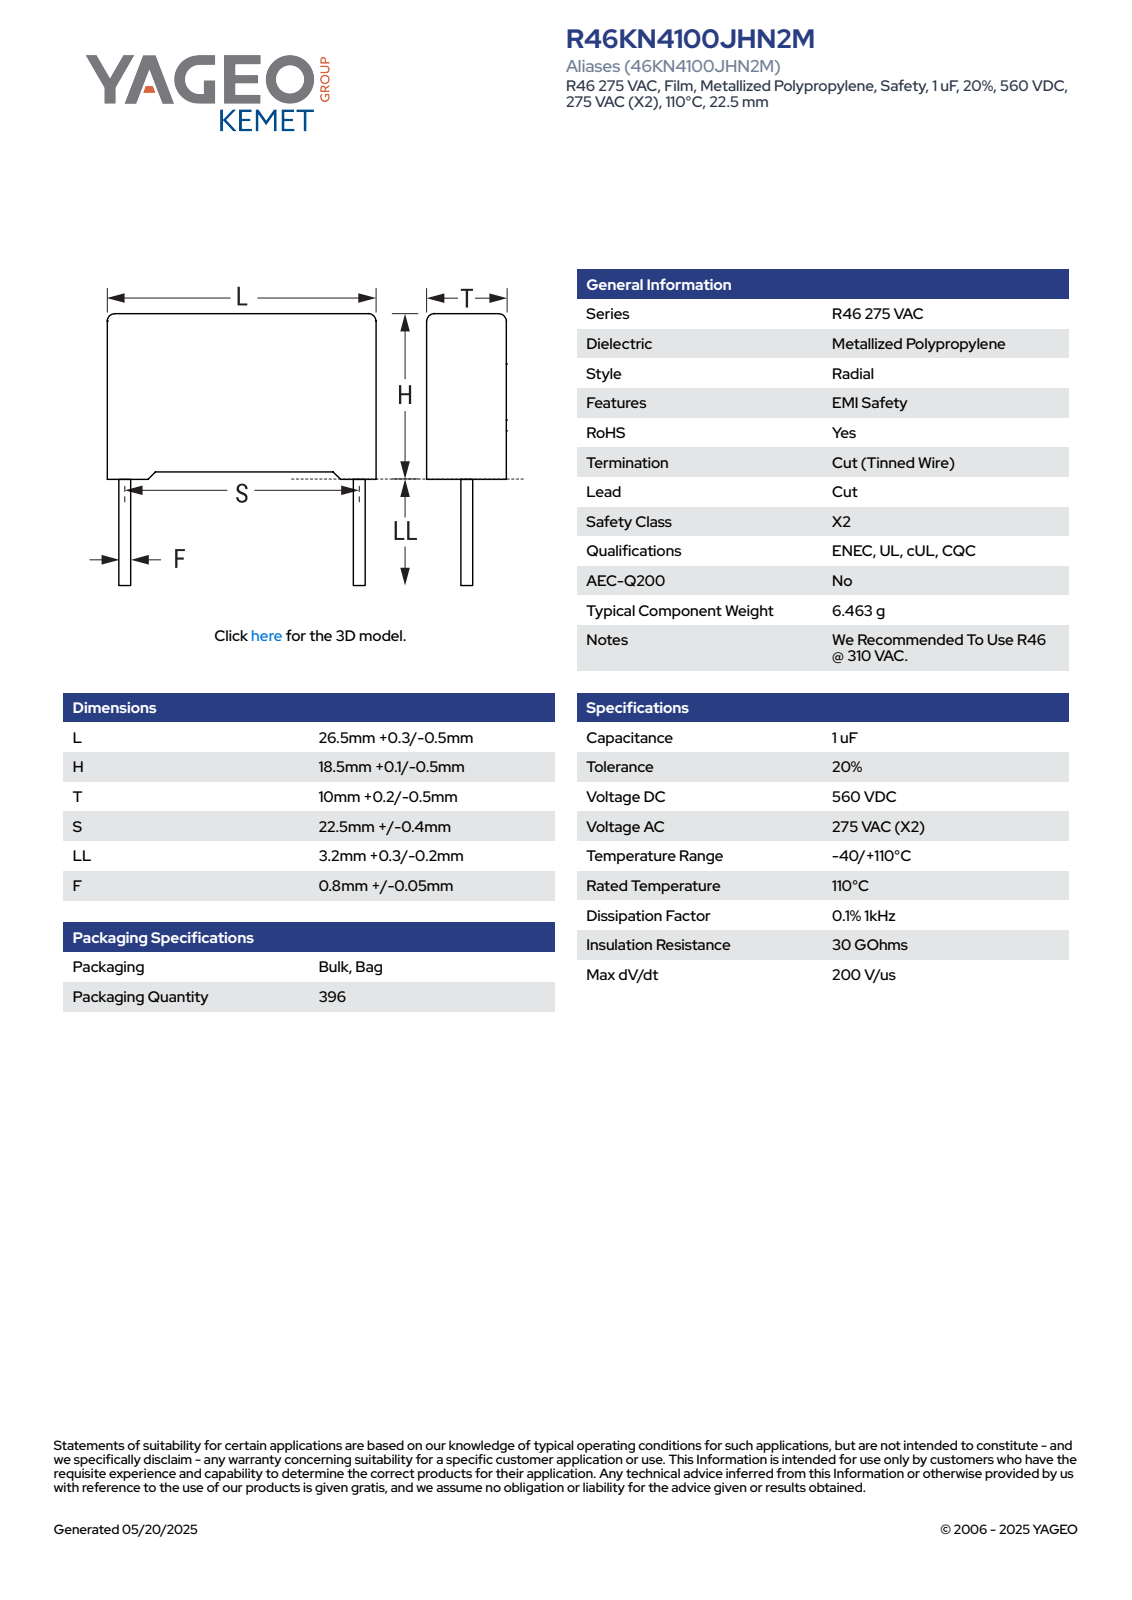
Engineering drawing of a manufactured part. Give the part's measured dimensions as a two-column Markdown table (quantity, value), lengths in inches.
| quantity | value |
| --- | --- |
| part name | CFR_RB2_26.5X18.5X10_L26.8H18.6T10.2S22.5LL3.5F0.85 |
| STEP written by | SolidWorks 2021 (AUTOMOTIVE_DESIGN) |
| units | inches |
| bodies | 4 solids, 85 faces (77 planar, 8 cylindrical, 0 other) |
| overall size | 1.055 × 0.87 × 0.402 |
| volume | 0.299 in³ |
| surface area | 3.08 in² |
| round bosses / shafts (diameter × count) | 0.033 × 2 |
| partial cylindrical surfaces (radius × count) | 0.02 × 4 |
| main face-to-face distances | 0.402, 0.703, 1.055, 0.707, 0.03, 0.025, 0.732, 0.035, 0.367, 1.02 |
